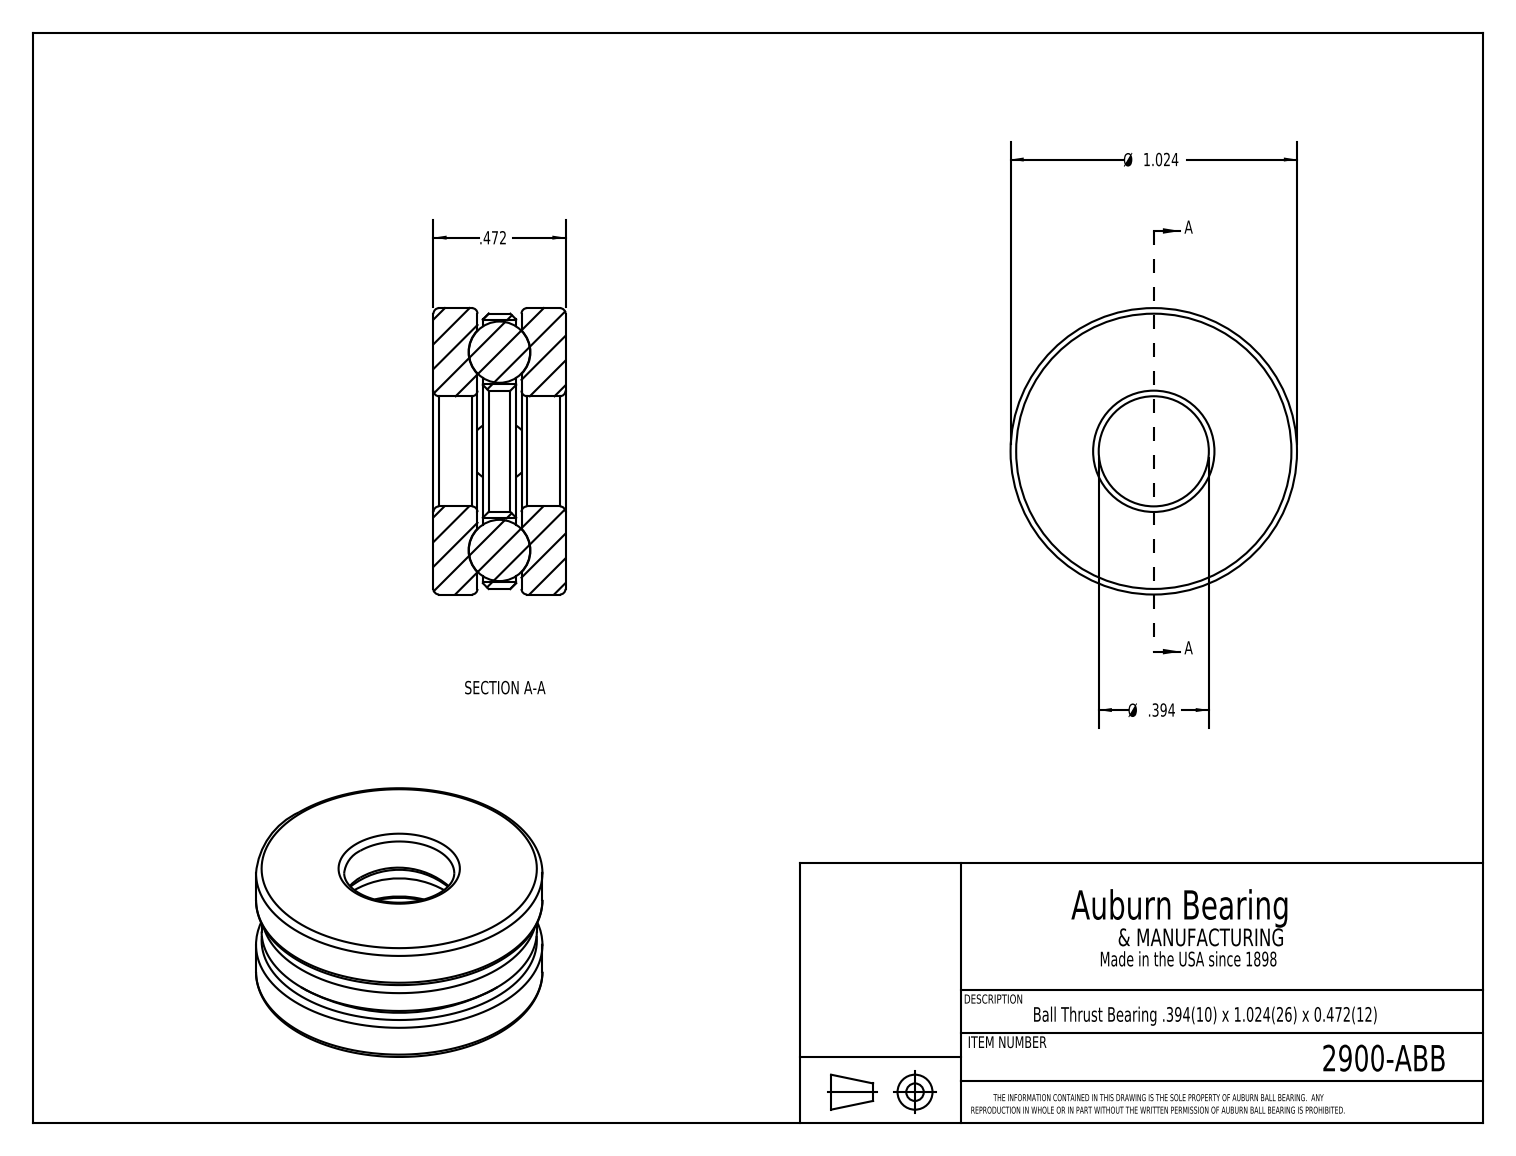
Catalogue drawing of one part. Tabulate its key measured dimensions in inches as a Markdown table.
| quantity | value |
| --- | --- |
| part name | 2900-ABB |
| STEP written by | SolidWorks 2017 (CONFIG_CONTROL_DESIGN) |
| units | inches |
| bodies | 7 solids, 36 faces (8 planar, 10 cylindrical, 18 other) |
| overall size | 1.024 × 1.024 × 0.472 |
| volume | 0.278 in³ |
| surface area | 6.386 in² |
| round holes (diameter × count) | 0.229 × 4, 0.394 × 1, 0.434 × 1 |
| round bosses / shafts (diameter × count) | 1.024 × 1, 0.984 × 1 |
| main face-to-face distances | 0.177, 0.295, 0.472, 0.157, 0.315, 0.02, 0.138, 0.118, 0.157 |
| hole center spacings | 0.354, 0.501, 0.709 |
